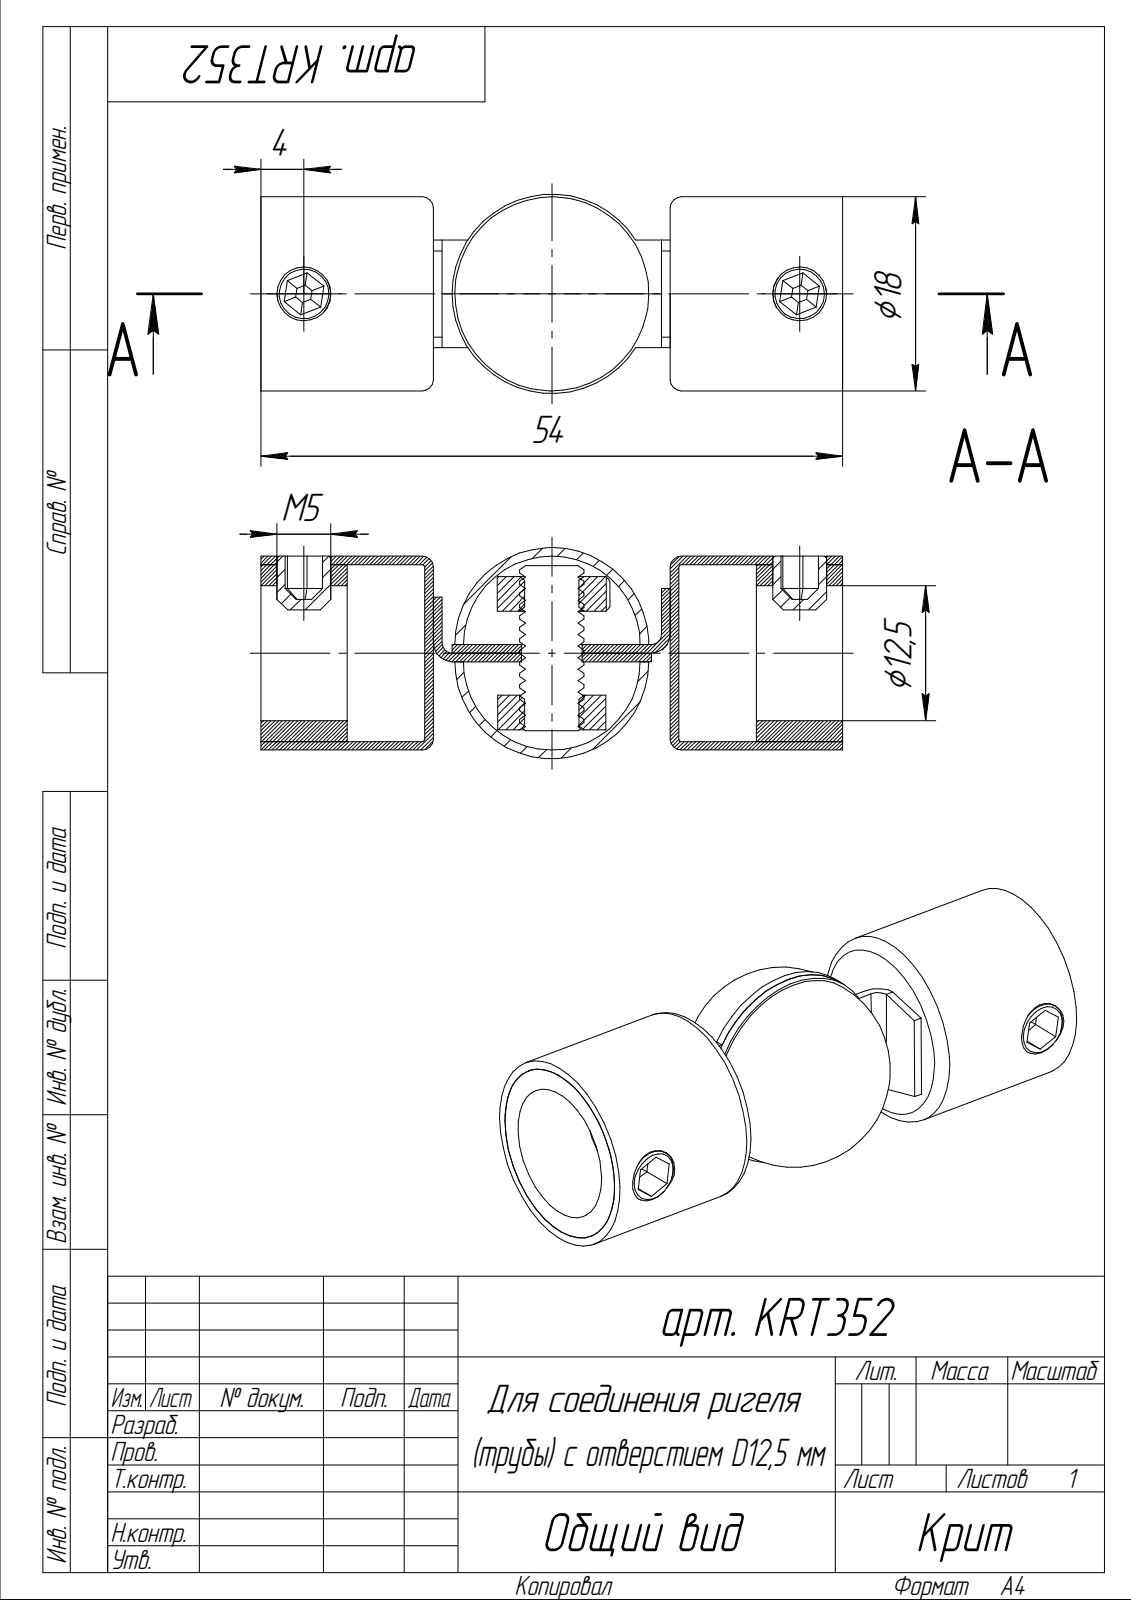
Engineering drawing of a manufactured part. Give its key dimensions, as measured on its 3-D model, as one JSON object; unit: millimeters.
{"part_name": "вставка; арт. KRT353.01; hex nut jam_am_B18.2.4.5M - Hex jam nut, M6 x 1 --D-N; M5_5 (+5 more)", "step_written_by": "SolidWorks 2014 (AUTOMOTIVE_DESIGN)", "units": "millimeters", "bodies": {"solids": 13, "faces": 274, "planar": 78, "cylindrical": 76, "other": 120}, "overall_size": [54, 19.6, 18.5], "volume_mm3": 5163, "surface_area_mm2": 10711, "round_holes": [[5, 3], [5.6, 1], [12.5, 1], [16.4, 1]], "round_bosses_or_shafts": [[18.5, 1], [18, 1], [6, 1]], "partial_cylinders_radius": [[1, 2], [1.8, 2]], "face_to_face_distances": [0.8, 22.8, 8, 1.6, 38, 22, 16, 15.2, 38.8, 23.6], "hole_center_spacings": [23, 46]}
